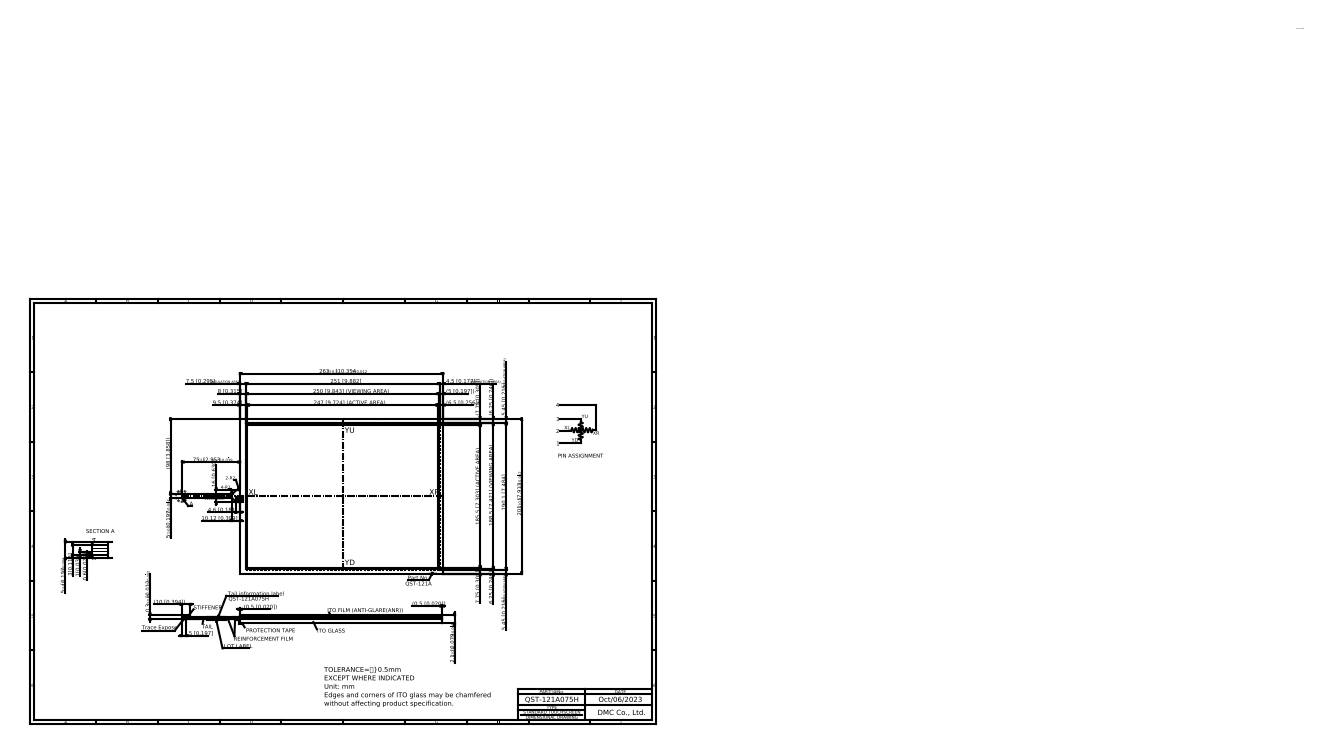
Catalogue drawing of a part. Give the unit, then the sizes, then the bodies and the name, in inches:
Units: inches
Overall size (bounding box): 15.378 × 11.079 × 0.087
Partial cylindrical surfaces — rounded edges, fillets, slot ends (radius × count): R0.02 ×2, R0.039 ×2, R0.079 ×2
Main face-to-face distances: 0.083, 0.079, 7.913, 0.071, 10.354, 0.075, 0.059, 0.016, 0.246, 7.667
Volume: 6.77 in³ · Surface area: 168.6 in²
Bodies: 1 solid, 51 faces (45 planar, 6 cylindrical, 0 other)
Part name (STEP PRODUCT): QST-121A075H
STEP written by: Autodesk Inventor 2020 (CONFIG_CONTROL_DESIGN)
